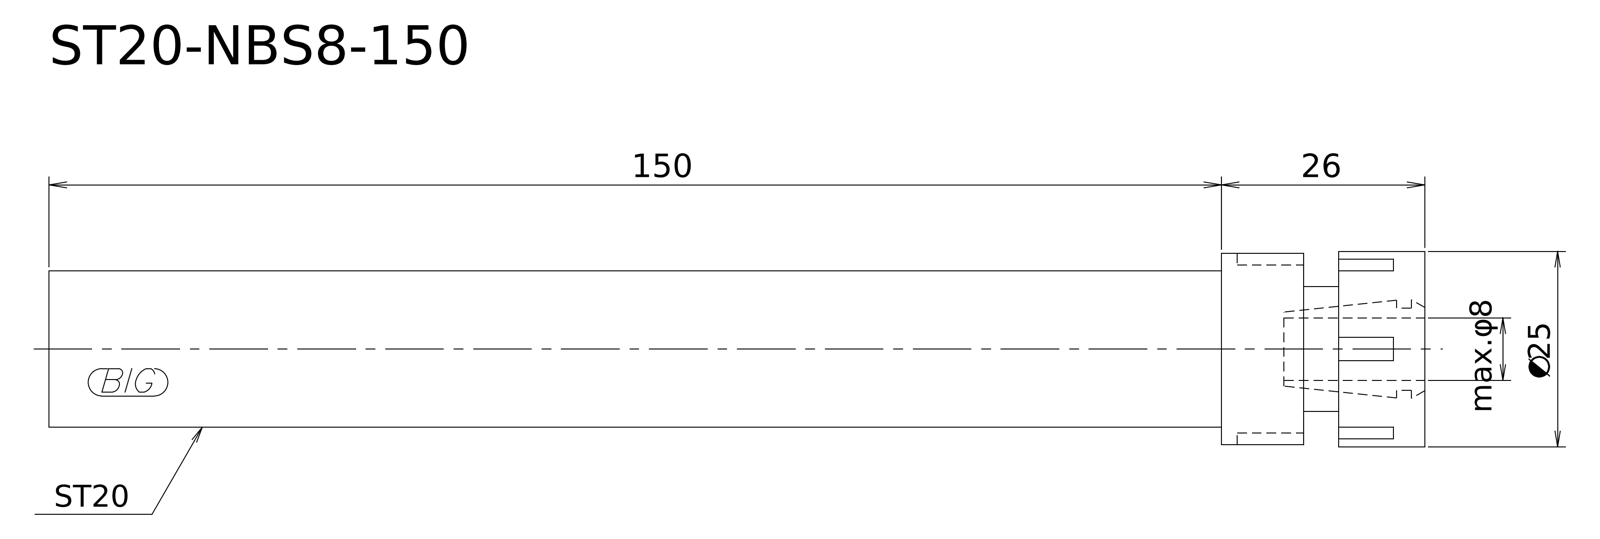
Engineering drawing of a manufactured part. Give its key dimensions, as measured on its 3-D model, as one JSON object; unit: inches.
{"step_written_by": "Kubotek KeyCreator V8.5.1 (14335) (CONFIG_CONTROL_DESIGN)", "units": "inches", "bodies": {"solids": 1, "faces": 9, "planar": 5, "cylindrical": 4, "other": 0}, "overall_size": [6.929, 0.984, 0.984], "volume_in3": 3.562, "surface_area_in2": 19.91, "round_bosses_or_shafts": [[0.984, 1], [0.965, 1], [0.787, 1], [0.63, 1]], "face_to_face_distances": [6.929, 0.433, 6.496, 0.61, 0.177, 6.319, 1.024, 0.591, 0.413, 5.906]}
